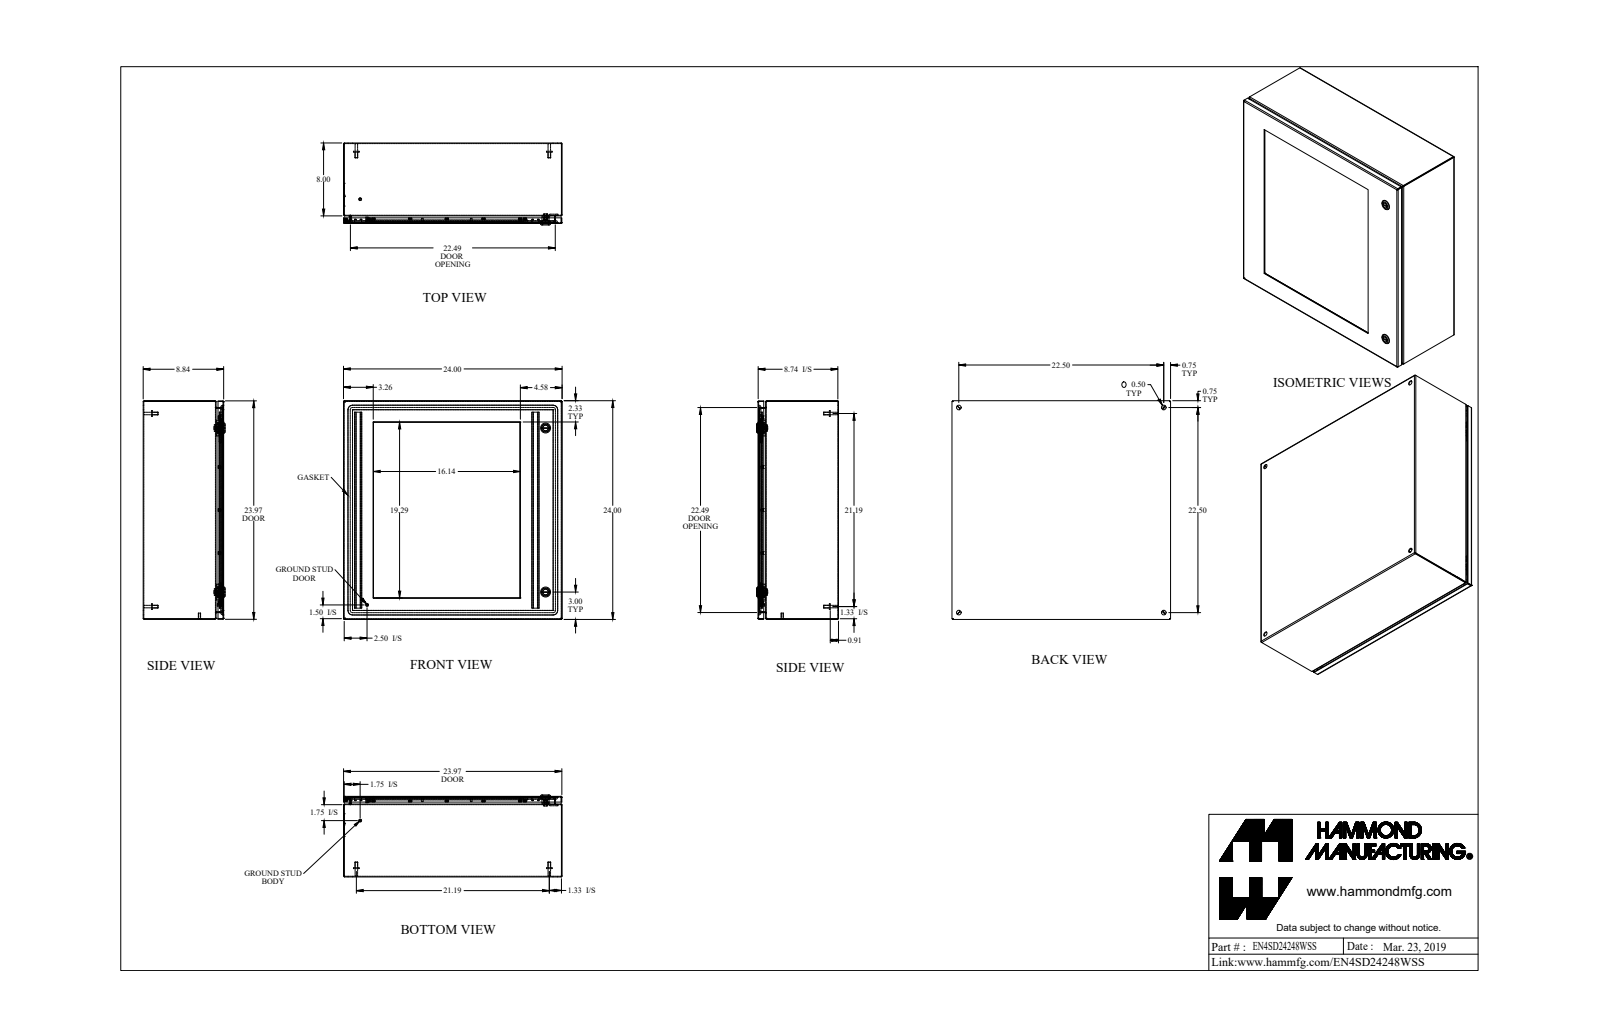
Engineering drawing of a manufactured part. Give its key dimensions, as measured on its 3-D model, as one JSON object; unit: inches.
{"part_name": "EN4SD24248WSS_Default", "step_written_by": "SolidWorks 2019 (CONFIG_CONTROL_DESIGN)", "units": "inches", "bodies": {"solids": 76, "faces": 1569, "planar": 819, "cylindrical": 466, "other": 284}, "overall_size": [24, 24, 8.997], "volume_in3": 230.8, "surface_area_in2": 4892, "round_holes": [[0.13, 20], [0.25, 18], [0.5, 6], [0.197, 2], [0.387, 2], [0.63, 2], [0.768, 2], [0.172, 1], [0.24, 1], [0.242, 1]], "round_bosses_or_shafts": [[0.368, 20], [0.226, 19], [0.164, 18], [0.625, 6], [0.313, 6], [0.275, 4], [1.1, 2], [0.785, 2]], "partial_cylinders_radius": [[0.036, 20], [0.108, 20], [0.25, 16], [0.01, 12], [0.048, 12], [0.125, 12], [0.006, 4], [0.016, 4]], "face_to_face_distances": [0.072, 8.765, 23.928, 8.693, 8.443, 0.25, 8.515, 23.856, 24, 0.322], "hole_center_spacings": [17.781, 4.719, 19.57, 21.03, 9.437, 14.156, 17.144, 0.892]}
